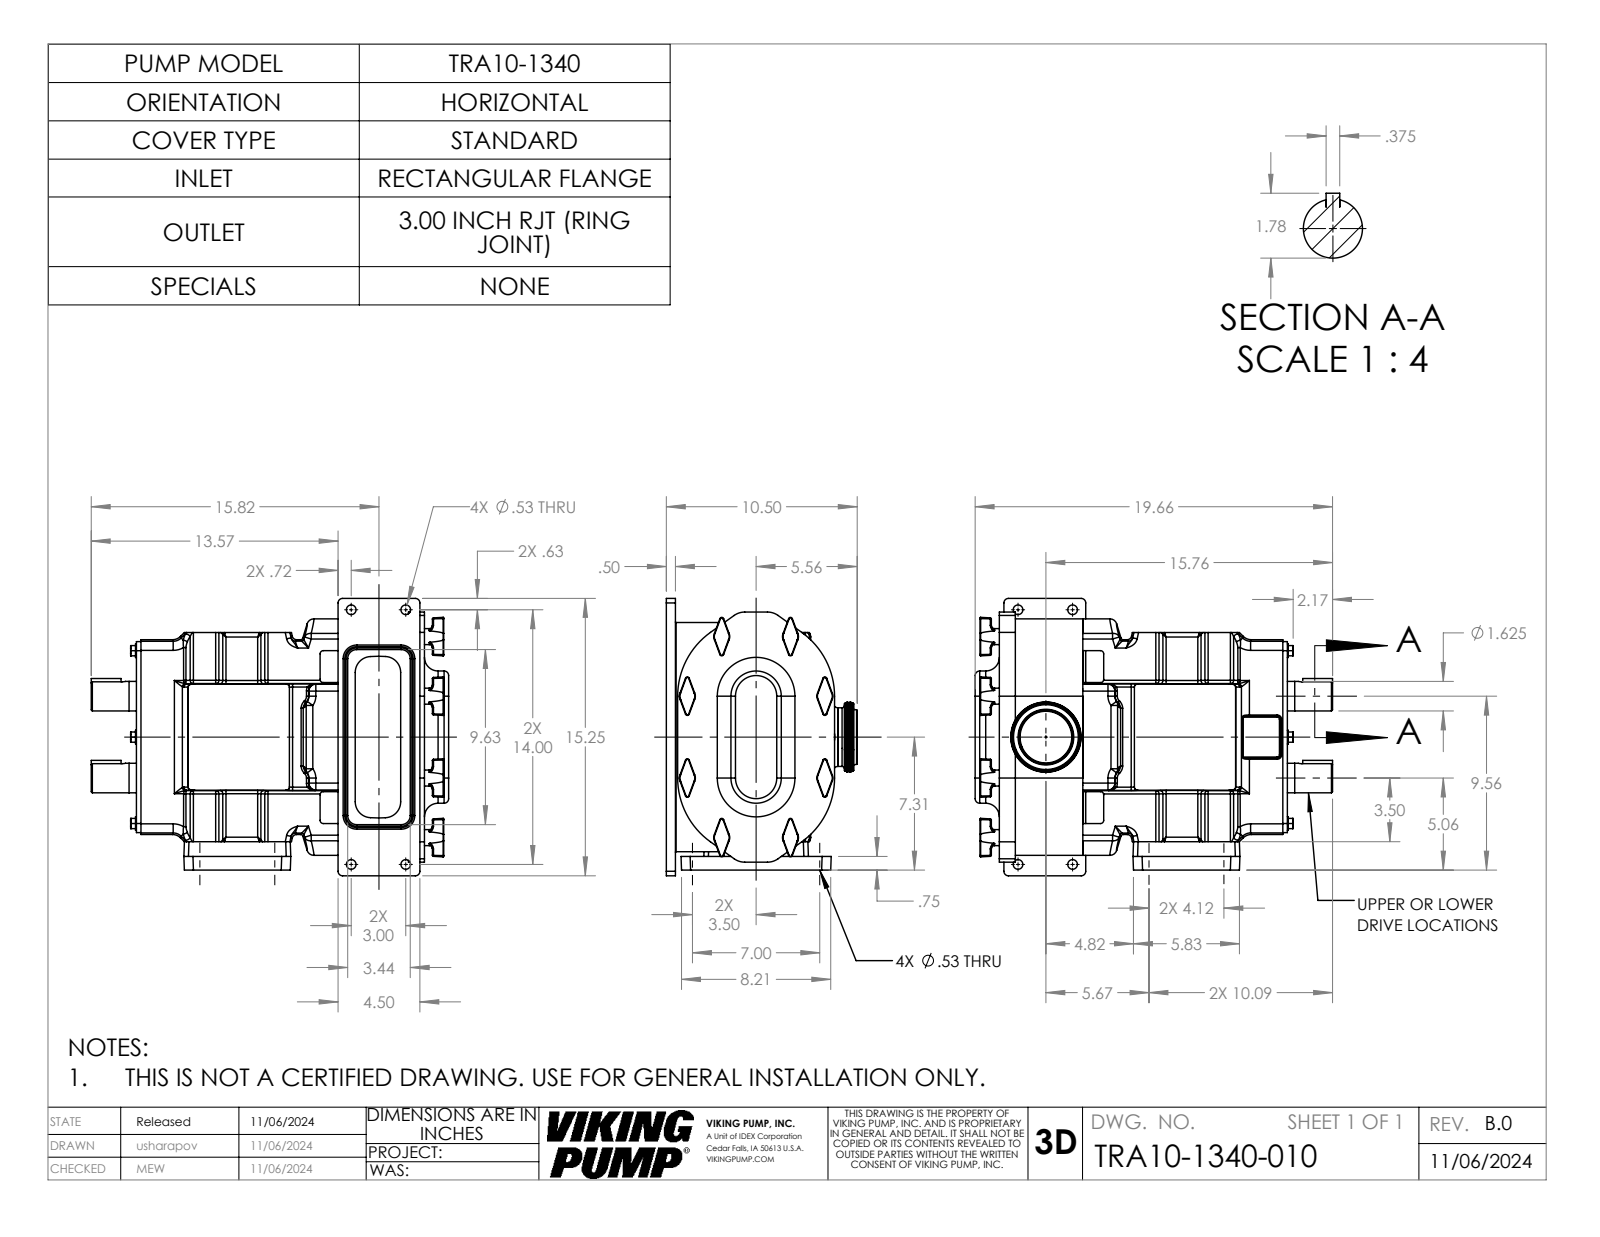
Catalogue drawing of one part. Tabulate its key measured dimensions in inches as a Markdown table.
| quantity | value |
| --- | --- |
| part name | TRA10-0600-COVER-STD; 1300RJT30; TRA10-1340-010; TRA10-1340-BODY (+1 more) |
| STEP written by | SolidWorks 2023 (AUTOMOTIVE_DESIGN) |
| units | inches |
| bodies | 4 solids, 1122 faces (303 planar, 399 cylindrical, 420 other) |
| overall size | 19.656 × 15.25 × 10.498 |
| volume | 1 334 in³ |
| surface area | 1 471 in² |
| round holes (diameter × count) | 0.531 × 8, 2.844 × 1, 2.868 × 1, 3.563 × 1 |
| round bosses / shafts (diameter × count) | 0.88 × 8, 0.75 × 6, 1.624 × 2, 3.224 × 1 |
| partial cylindrical surfaces (radius × count) | 0.18 × 44, 0.06 × 43, 0.03 × 36, 0.25 × 36, 0.38 × 28, 0.5 × 26, 0.12 × 24, 0.09 × 16 |
| main face-to-face distances | 3.711, 0.5, 0.88, 4.591, 0.36, 15.841, 14.961, 11.25, 6.5, 1.437 |
| hole center spacings | 3, 4.12, 7, 7.152, 7.166, 8.122, 14, 14.318 |
